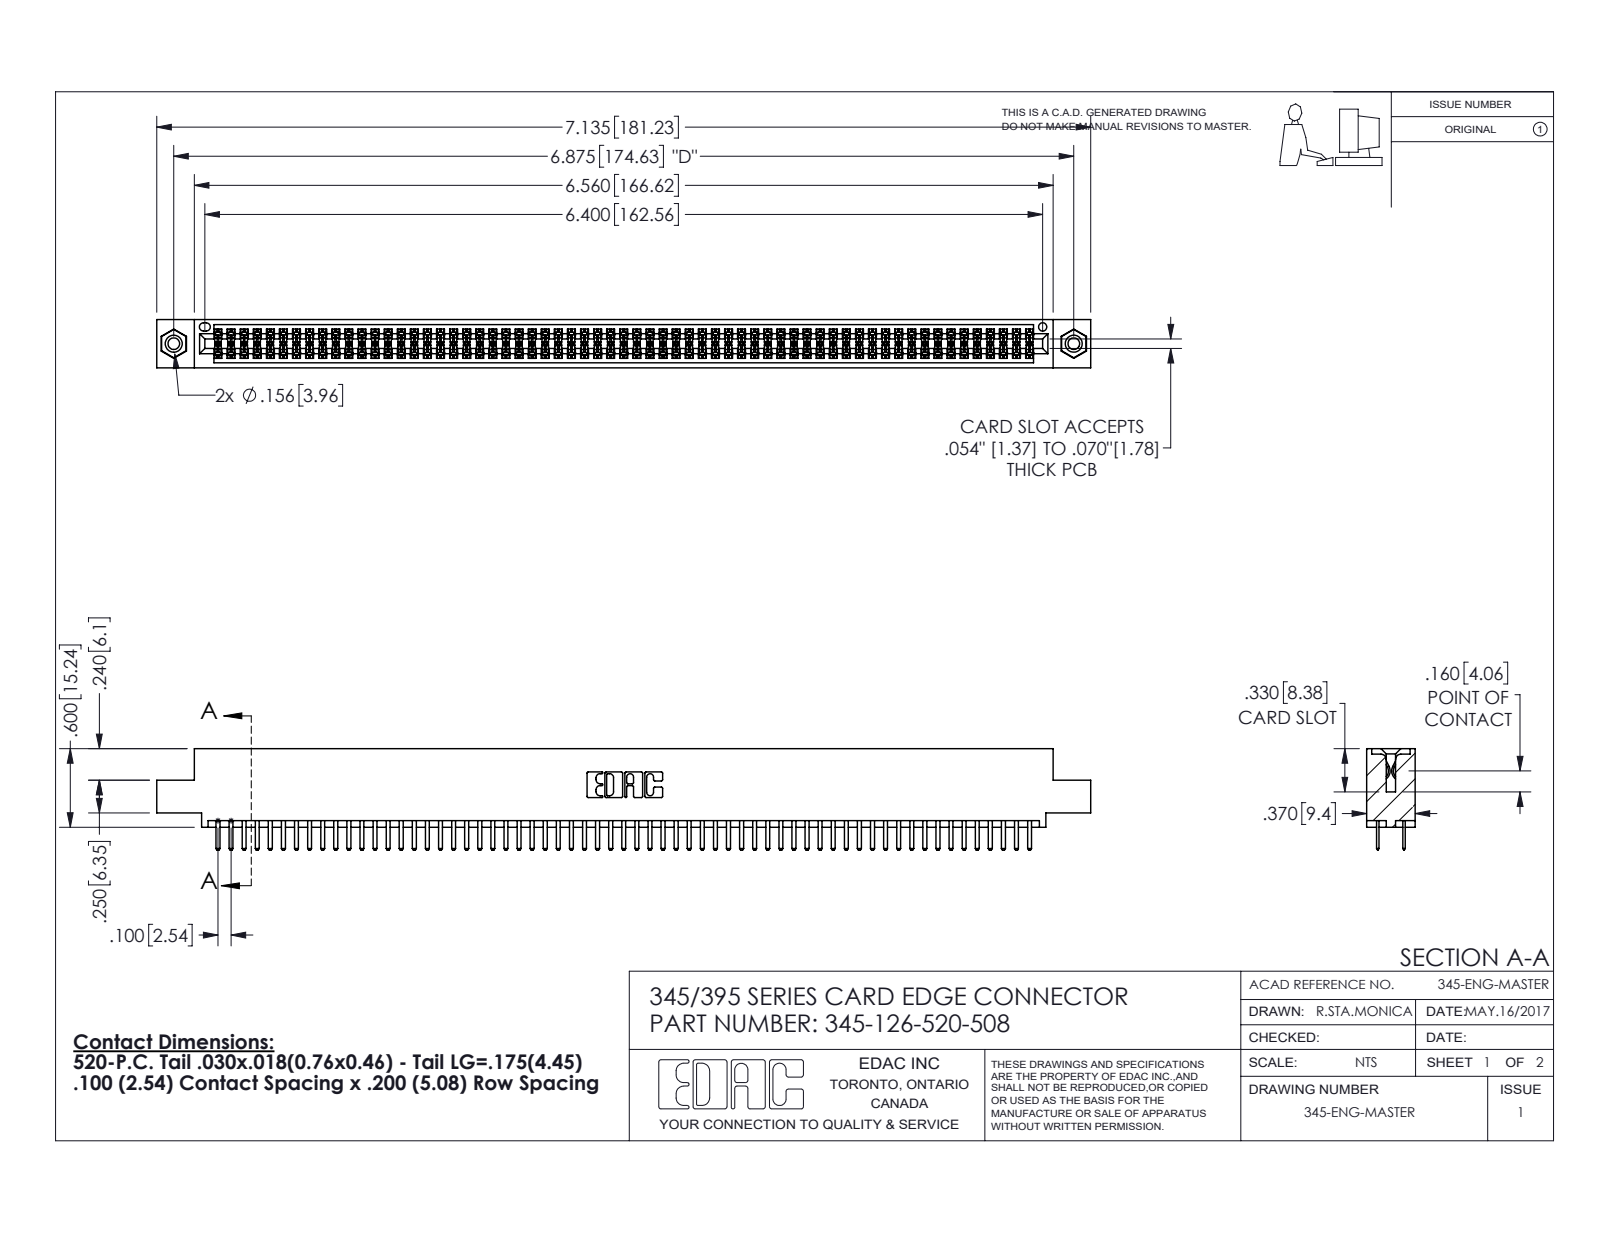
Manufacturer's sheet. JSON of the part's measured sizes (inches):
{"part_name": "345-250-001_345-250-003-102; 345-126-520-508; 345-292-001_345-293-120; 345 Part_0.110 Offset - 0.156 Dia-TI", "step_written_by": "SolidWorks 2016 (CONFIG_CONTROL_DESIGN)", "units": "inches", "bodies": {"solids": 129, "faces": 6994, "planar": 4526, "cylindrical": 2452, "other": 16}, "overall_size": [7.135, 0.775, 0.37], "volume_in3": 1.078, "surface_area_in2": 41.08, "round_holes": [[0.089, 2], [0.125, 2], [0.156, 2], [0.064, 1]], "round_bosses_or_shafts": [[0.155, 2]], "partial_cylinders_radius": [[0.006, 189], [0.01, 130], [0.01, 22], [0.007, 6], [0.031, 6], [0.026, 3], [0.014, 2], [0.019, 2]], "face_to_face_distances": [0.072, 0.298, 0.2, 0.37, 0.098, 0.272, 0.025, 0.225, 0.022, 0.072], "hole_center_spacings": [0.27, 6.639, 6.875]}
